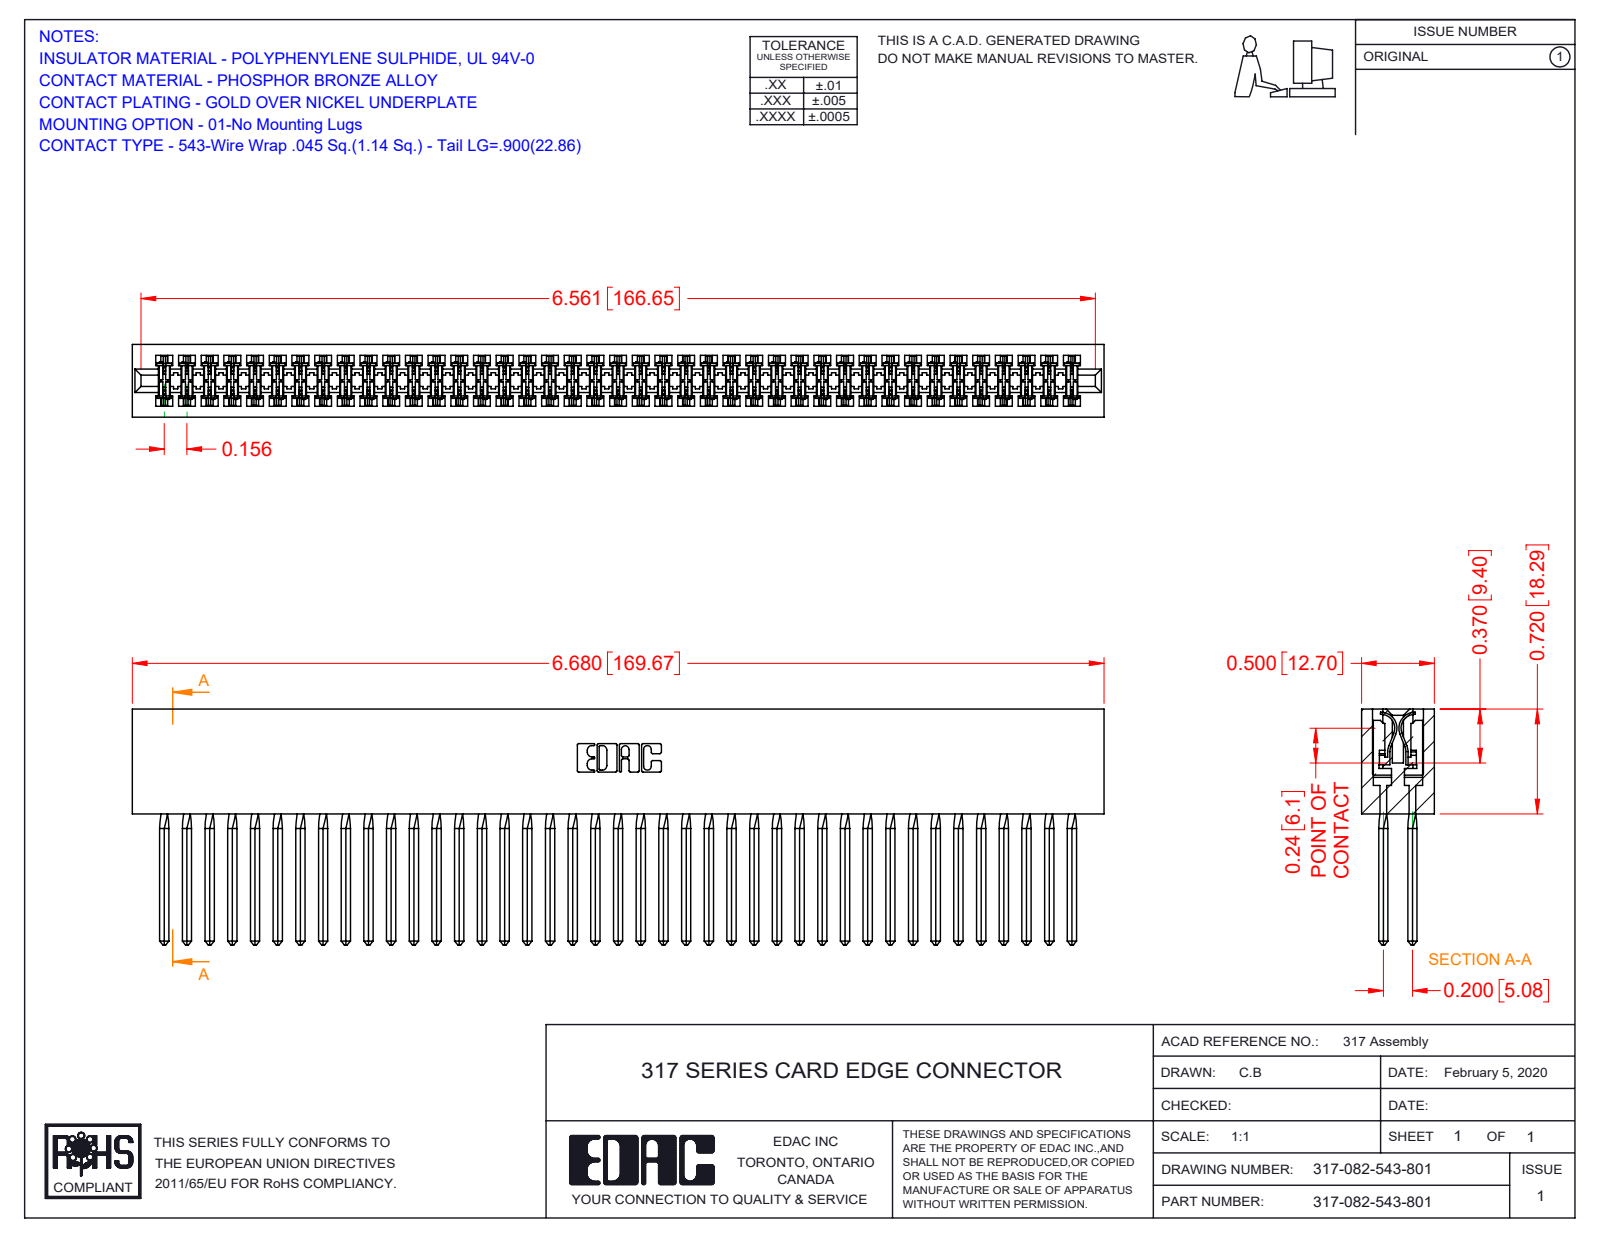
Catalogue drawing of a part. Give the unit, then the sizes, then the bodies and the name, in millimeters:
Units: millimetres
Overall size (bounding box): 169.7 × 41.1 × 12.7
Partial cylindrical surfaces — rounded edges, fillets, slot ends (radius × count): R0.4 ×164, R0.3 ×22, R0.2 ×6, R0.8 ×6, R0.7 ×3, R2.4 ×2, R2.5 ×2, R2.8 ×2
Main face-to-face distances: 1.9, 12.7, 10.8, 8.9, 5, 2.8, 2.4, 5.1, 2.9, 3.3
Volume: 30 640 mm³ · Surface area: 46 730 mm²
Bodies: 83 solids, 7388 faces (6036 planar, 1024 cylindrical, 328 other)
Part name (STEP PRODUCT): 317 Part_Lugless; 317-290-001_543; 317-082-543-801
STEP written by: SolidWorks 2016 (CONFIG_CONTROL_DESIGN)
